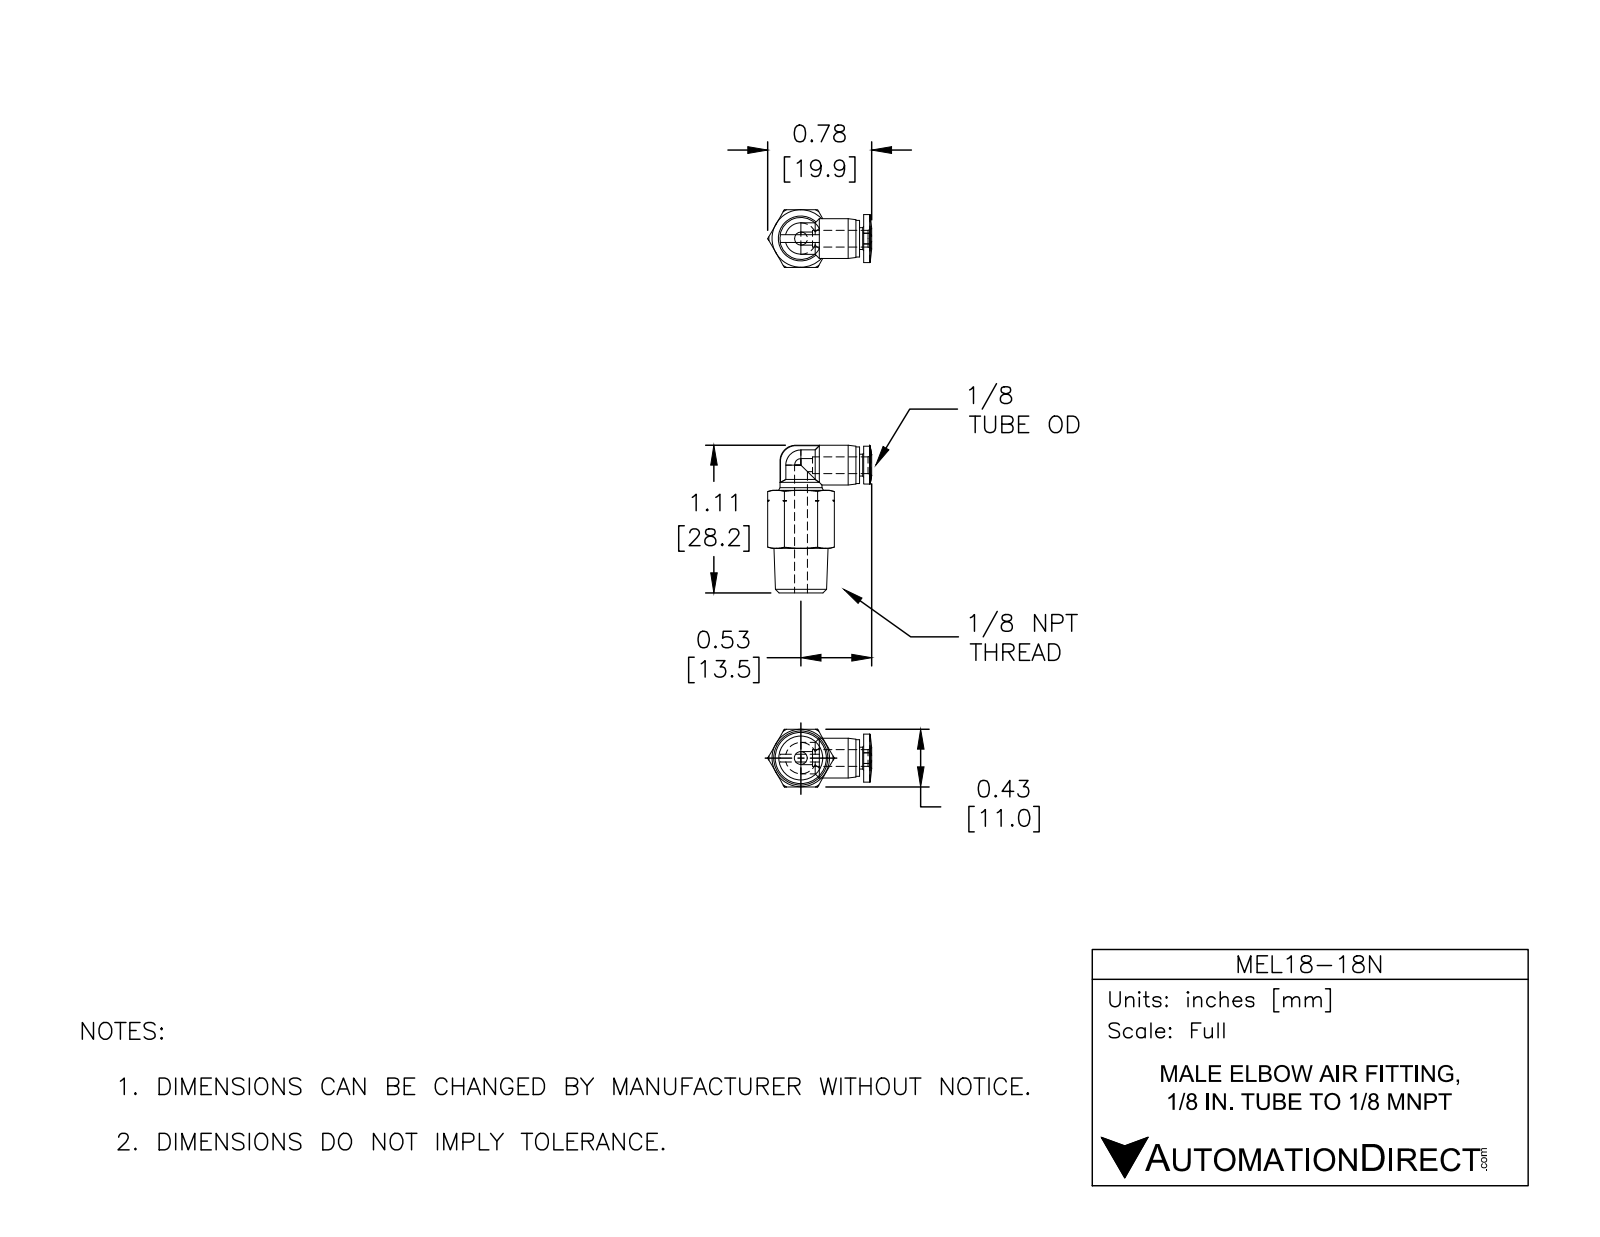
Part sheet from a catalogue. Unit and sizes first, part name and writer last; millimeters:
Units: millimetres
Overall size (bounding box): 28.2 × 19.9 × 11
Round holes (diameter × count): ⌀2.5 ×2, ⌀3.2 ×1
Round bosses / shafts (diameter × count): ⌀8 ×1, ⌀7.6 ×1, ⌀7 ×1, ⌀4.2 ×1
Partial cylindrical surfaces — rounded edges, fillets, slot ends (radius × count): R3 ×2, R3.6 ×2
Main face-to-face distances: 11, 19.6, 0.8, 4.7, 6.2, 1.5, 8.5, 11.1, 9, 9.8
Volume: 2 330 mm³ · Surface area: 1 672 mm²
Bodies: 1 solid, 101 faces (18 planar, 20 cylindrical, 63 other)
Part name (STEP PRODUCT): MEL18-18N
STEP written by: SolidWorks 2015 (CONFIG_CONTROL_DESIGN)
